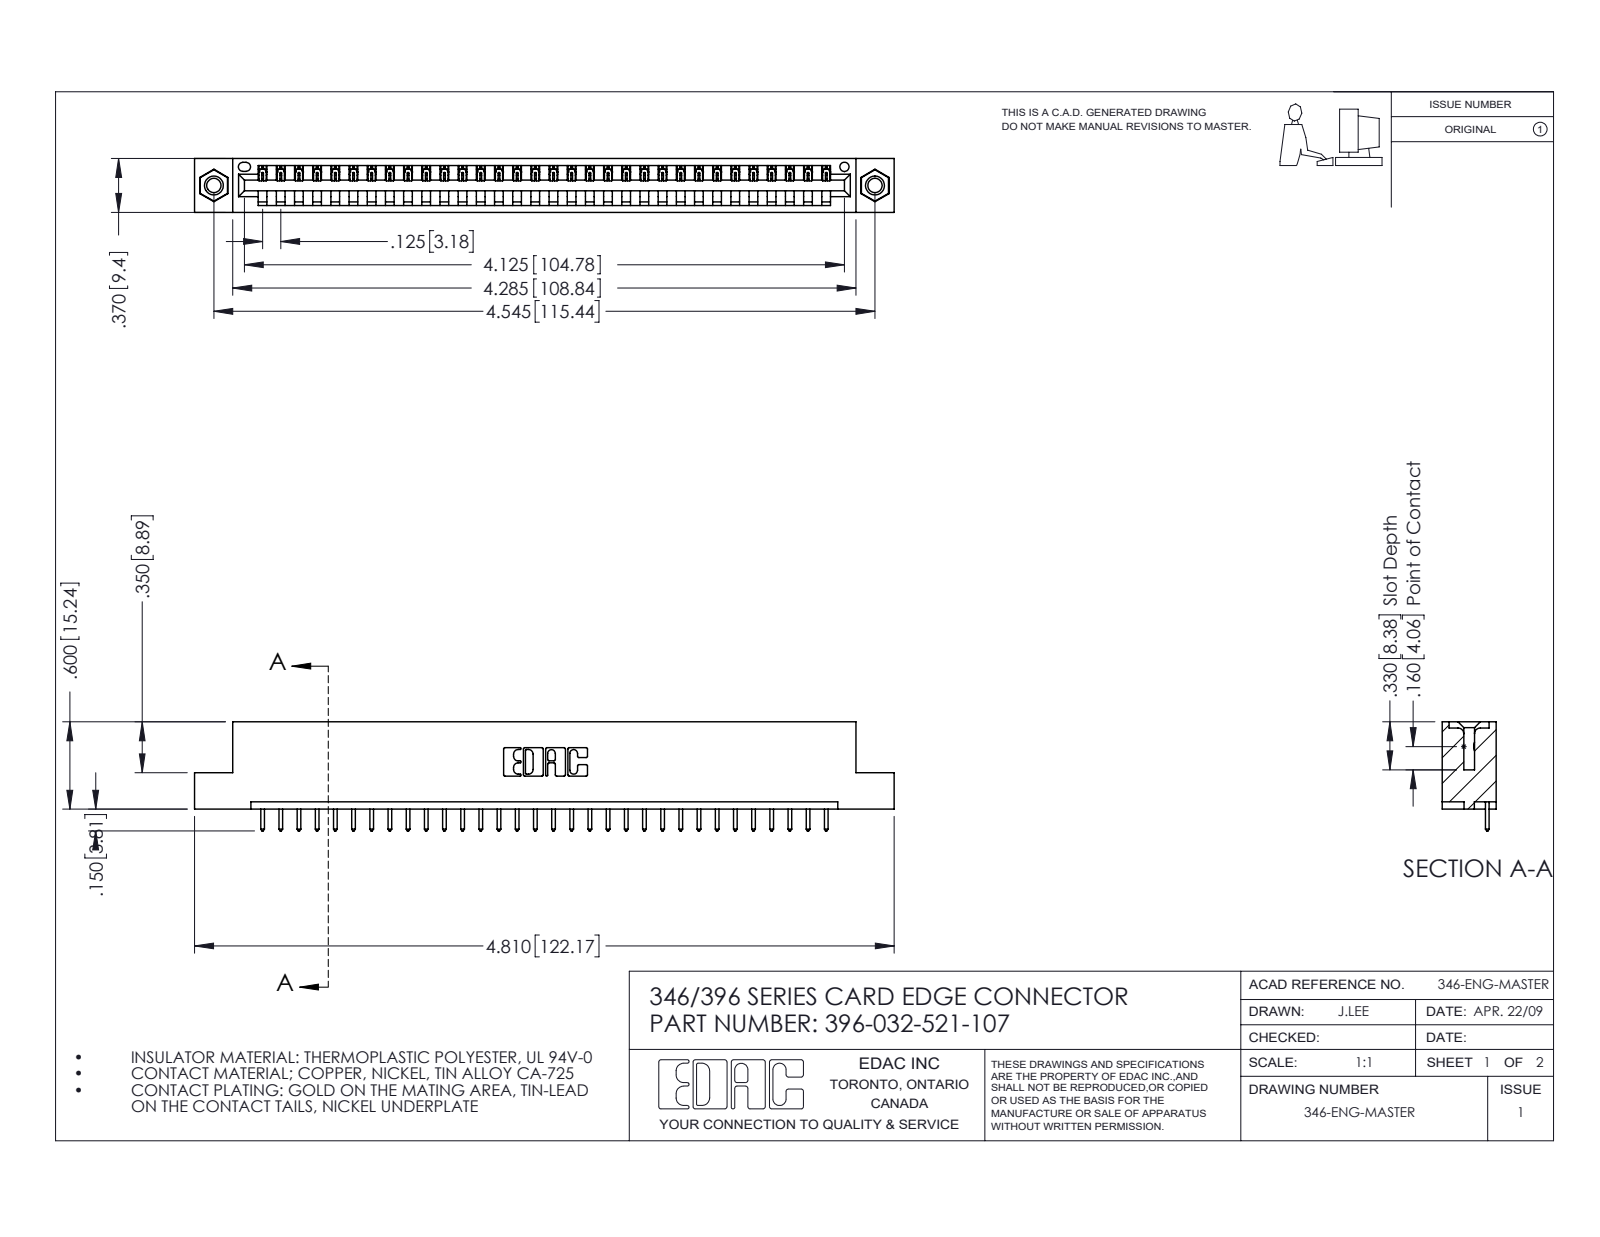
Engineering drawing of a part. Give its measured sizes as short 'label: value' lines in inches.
name: 396-032-521-107; 346 Part_Flush Mounting Lugs - 0.156 Dia-TI; 345-250-001_345-250-005-103; 345-292-001_345-293-121
written by: SolidWorks 2016 (CONFIG_CONTROL_DESIGN)
unit: in
bodies: 35 solids, 2038 faces (1388 planar, 634 cylindrical, 16 other)
size: 4.81 × 0.75 × 0.37
volume: 0.703 in³; area: 21.65 in²
holes: 2× ⌀0.098, 2× ⌀0.125, 2× ⌀0.156, 1× ⌀0.064
bosses: 2× ⌀0.155
rounds: 64× R0.006, 64× R0.01, 22× R0.01, 6× R0.007, 6× R0.031, 3× R0.026, 2× R0.031, 2× R0.04
face distances: 0.048, 0.322, 0.37, 0.25, 0.072, 0.298, 0.025, 0.148, 0.222, 0.1
hole spacings: 0.246, 4.337, 4.545
